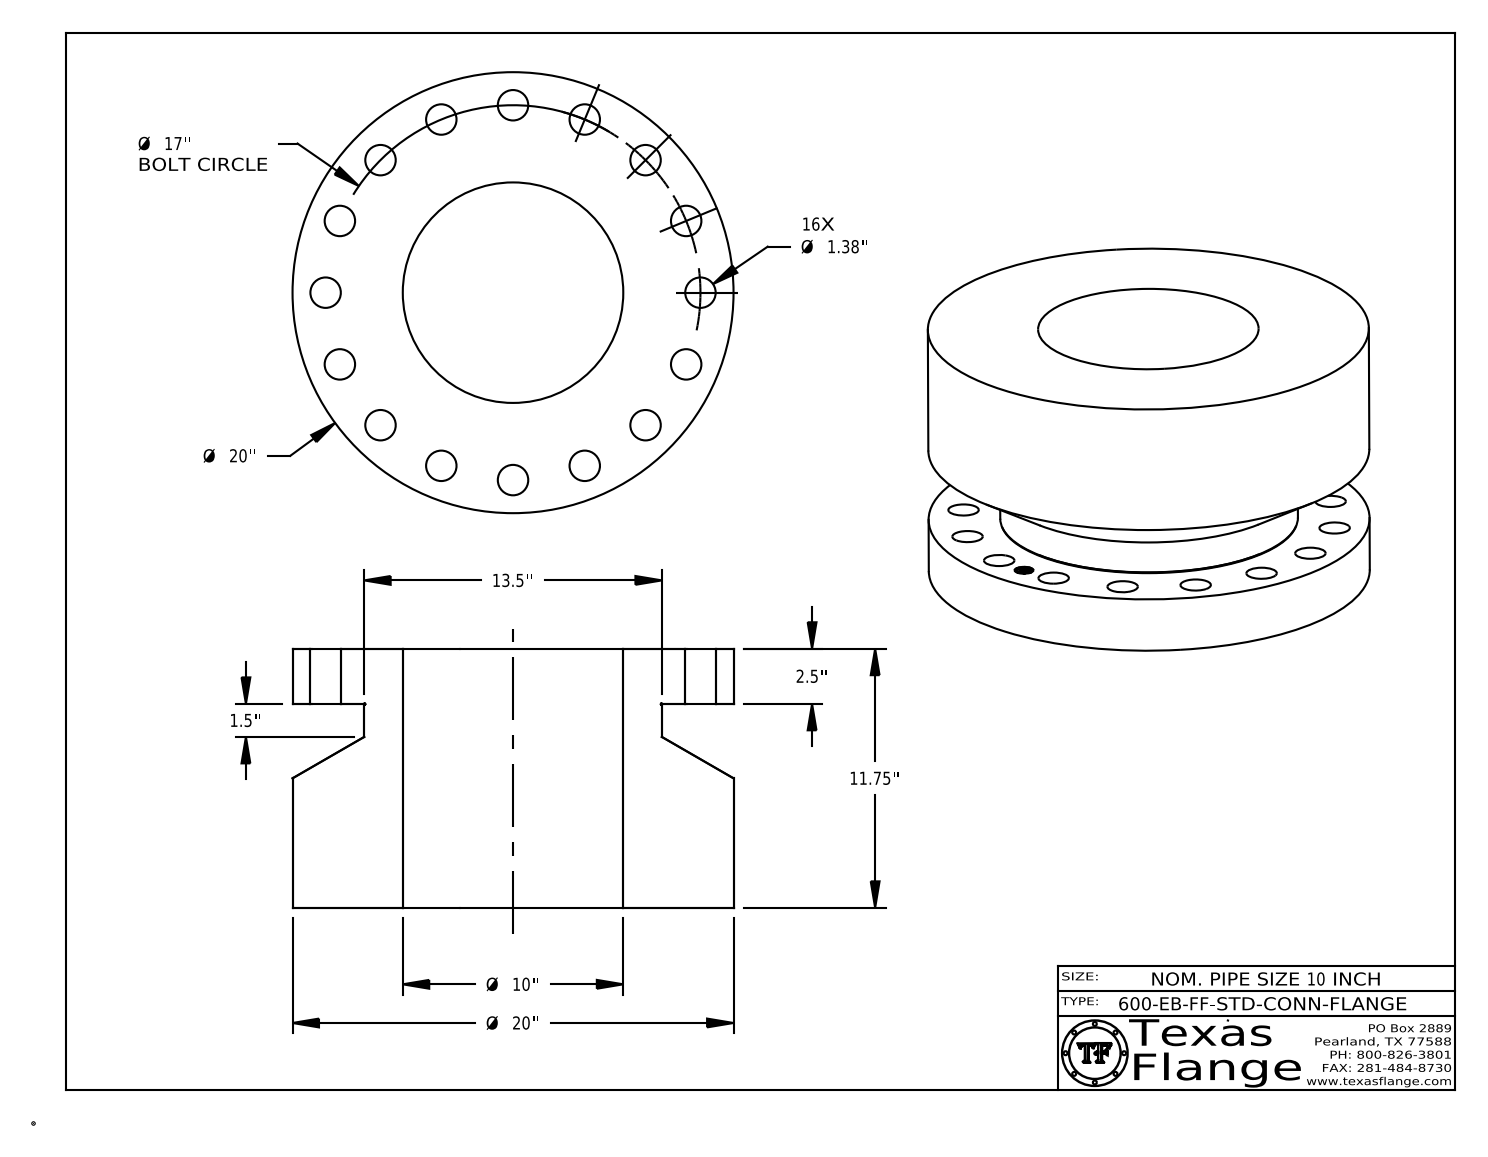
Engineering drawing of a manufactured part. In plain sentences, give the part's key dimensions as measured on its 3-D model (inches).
The part is named "10-600-EB-FF-STD-CONN-FLANGE". Its 3-D file was written by "CATIA V5 STEP AP214 (AUTOMOTIVE_DESIGN)". It is 1 solid with 434 faces: 368 planar, 60 cylindrical and 6 other. Overall it measures 20 by 20 by 11.75 inches. Its volume is 2 281 cubic inches and its surface area 1 926 square inches. Round holes: 16 of diameter 1.38, 1 of diameter 0.85, 1 of diameter 10. Round bosses or shafts: 8 of diameter 0.051, 1 of diameter 20, 1 of diameter 13.5, 1 of diameter 0.67. The main face-to-face distances are 11.75, 2.5, 9.25, 2.495, 9.255, 0.254, 0.249, 0.016, 0.046, 0.165. The hole center spacings are 3.317, 14.135, 8.5, 6.506, 12.021, 9.444, 9.445, 15.706.
